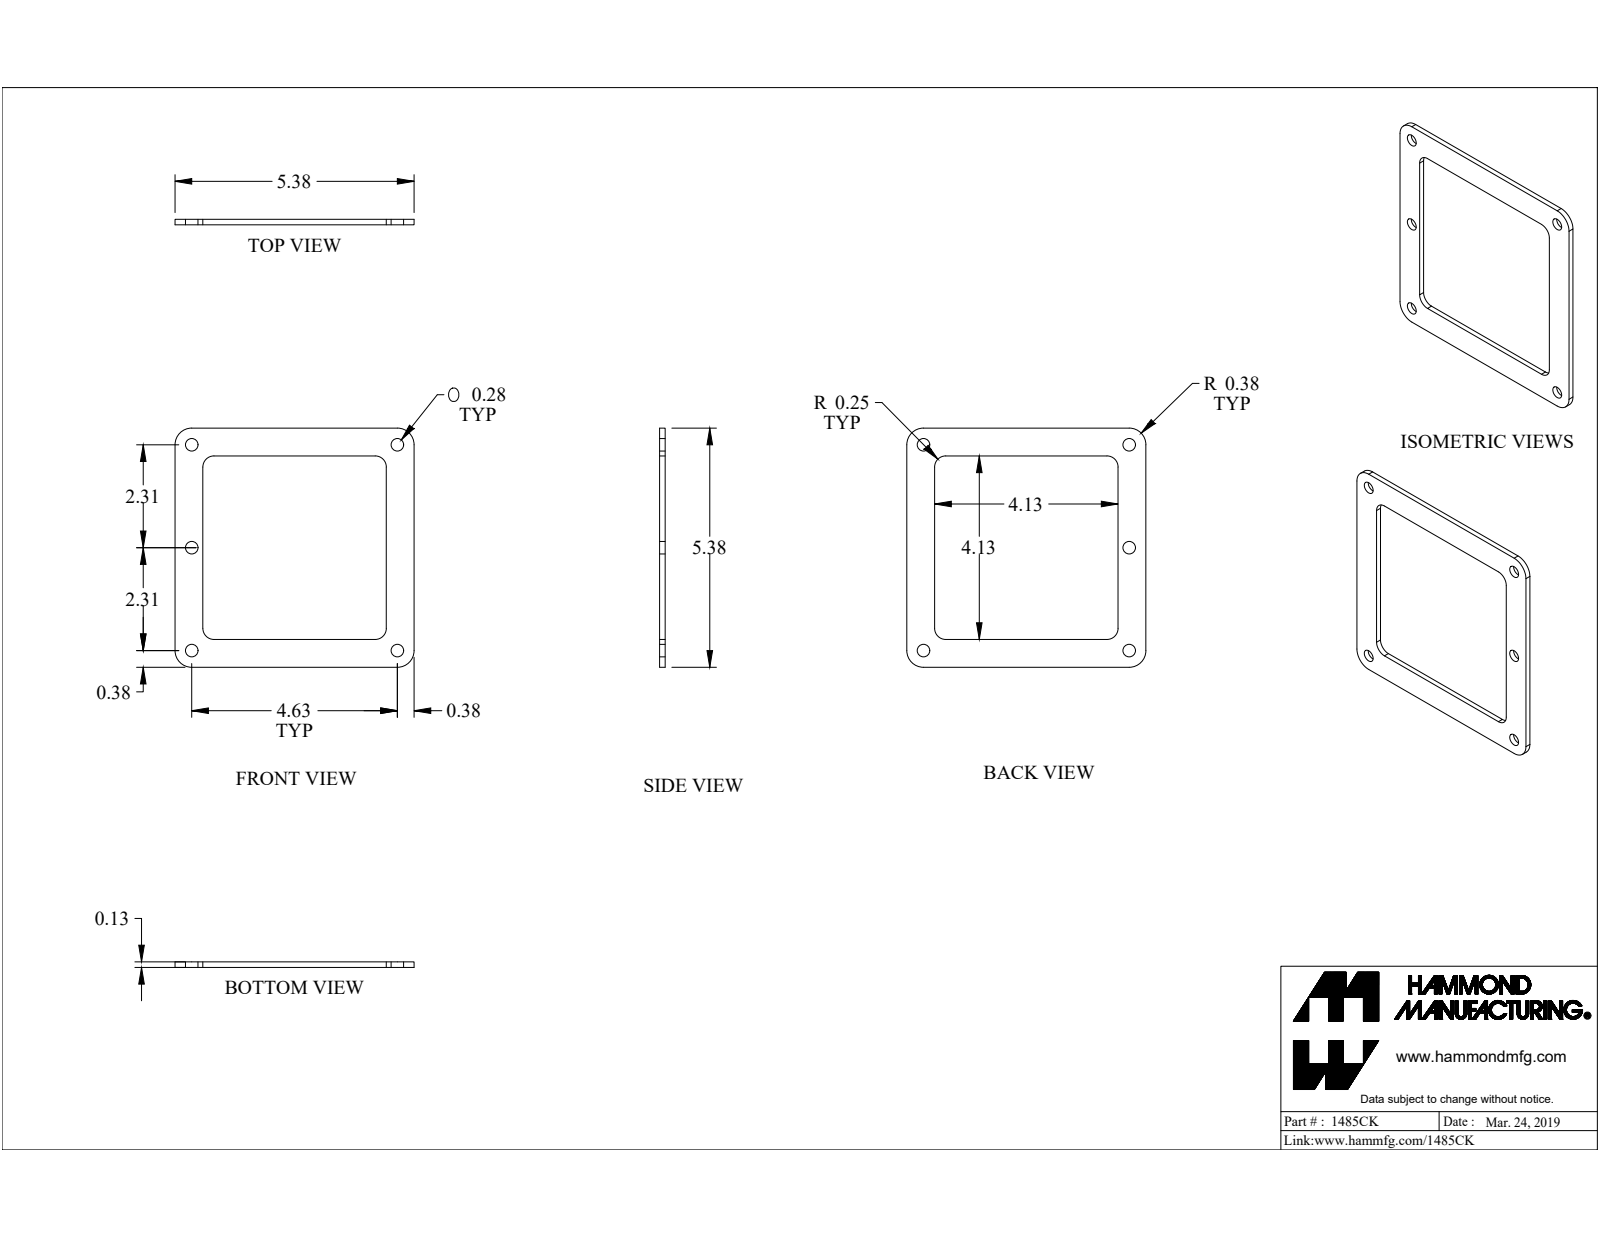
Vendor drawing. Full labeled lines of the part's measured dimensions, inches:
Part name (STEP PRODUCT): 1485CK
STEP written by: SolidWorks 2019 (CONFIG_CONTROL_DESIGN)
Units: inches
Bodies: 1 solid, 23 faces (10 planar, 13 cylindrical, 0 other)
Overall size (bounding box): 5.375 × 5.375 × 0.125
Volume: 1.437 in³ · Surface area: 28.16 in²
Round holes (diameter × count): ⌀0.281 ×5
Partial cylindrical surfaces — rounded edges, fillets, slot ends (radius × count): R0.25 ×4, R0.375 ×4
Main face-to-face distances: 0.125, 0.625, 4.75, 5.375, 4.125
Hole centre spacings: 4.625, 2.313, 5.171, 6.541
